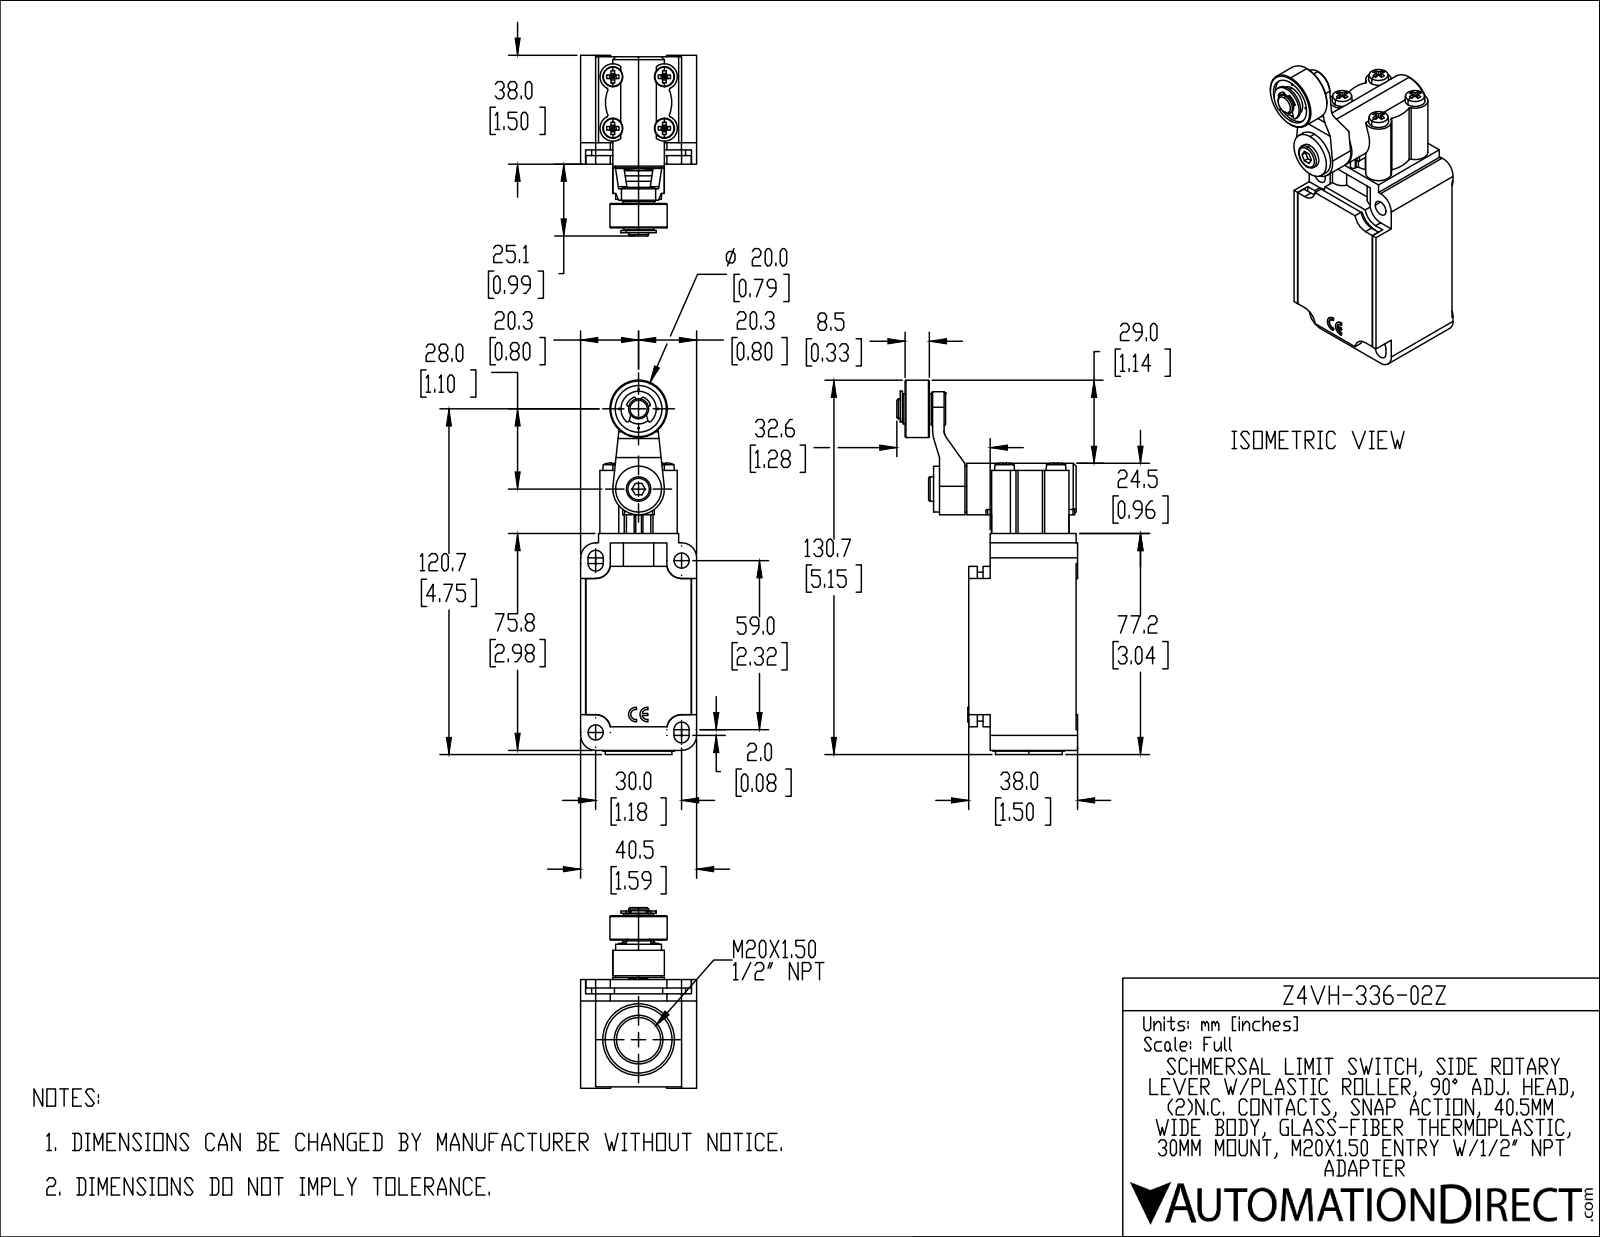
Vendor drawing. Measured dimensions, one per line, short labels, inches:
name: Z4VH-336-02Z
written by: SolidWorks 2019 (AUTOMOTIVE_DESIGN)
unit: in
bodies: 1 solid, 421 faces (230 planar, 151 cylindrical, 40 other)
size: 5.146 × 2.484 × 1.594
volume: 7.66 in³; area: 39.18 in²
holes: 4× ⌀0.02, 2× ⌀0.209, 1× ⌀0.224, 1× ⌀0.642, 1× ⌀0.65, 1× ⌀0.669
bosses: 1× ⌀0.984, 1× ⌀0.917, 1× ⌀0.787, 1× ⌀0.709, 1× ⌀0.63, 1× ⌀0.413, 1× ⌀0.335, 1× ⌀0.276
rounds: 16× R0.024, 8× R0.205, 8× R0.207, 4× R0.104, 4× R0.177, 4× R0.283, 3× R0.039, 3× R0.157
face distances: 1.594, 1.476, 0.295, 1.181, 0.079, 0.177, 1.28, 0.069, 1.526, 0.118
hole spacings: 0.266, 0.376, 0.531, 1.134, 0.837, 1.102, 1.148, 1.368
